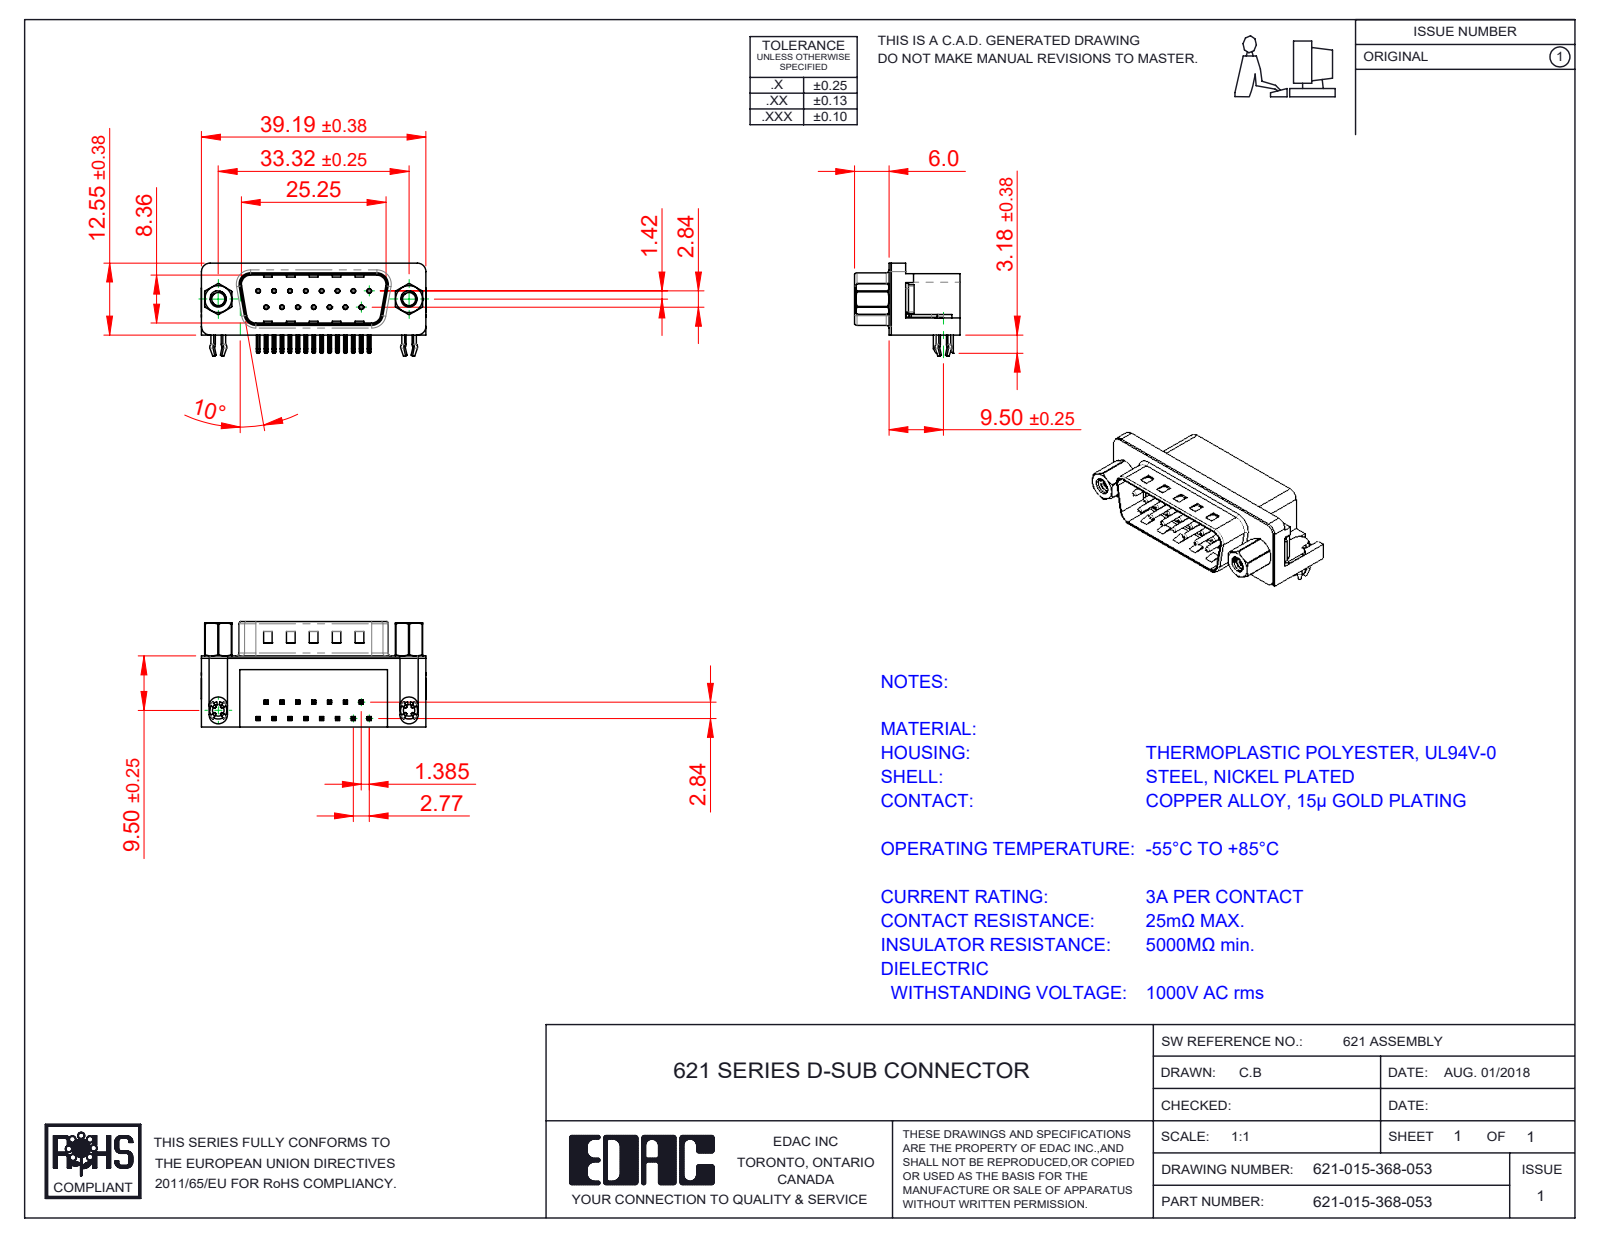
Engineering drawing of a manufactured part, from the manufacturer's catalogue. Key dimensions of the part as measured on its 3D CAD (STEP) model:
Part name (STEP PRODUCT): 621 Contact Bottom; 621 Shell_15 Socket; 621 Housing_15 Socket; 621 4-40 Threaded Rivet (+4 more)
STEP written by: SolidWorks 2016 (CONFIG_CONTROL_DESIGN)
Units: millimetres
Bodies: 23 solids, 1633 faces (915 planar, 529 cylindrical, 189 other)
Overall size (bounding box): 39.22 × 18.4 × 15.73
Volume: 4 640 mm³ · Surface area: 6 212 mm²
Round holes (diameter × count): ⌀0.35 ×15, ⌀0.8 ×15, ⌀2.26 ×4, ⌀2.29 ×2, ⌀4 ×2, ⌀4.8 ×2, ⌀5 ×2
Round bosses / shafts (diameter × count): ⌀0.75 ×15, ⌀4.9 ×2, ⌀4.75 ×2, ⌀3.9 ×2, ⌀3.26 ×2, ⌀2.79 ×2
Partial cylindrical surfaces — rounded edges, fillets, slot ends (radius × count): R0.25 ×68, R0.12 ×30, R1 ×16, R0.5 ×9, R1.6 ×8, R1.5 ×6, R0.9 ×4, R2 ×4
Main face-to-face distances: 0.4, 12, 10.35, 12.4, 2.1, 10.46, 1.7, 10.86, 8.76, 9.5
Hole centre spacings: 3.16, 2.77, 5.54, 8.31, 11.08, 5.03, 5.04, 7.48
